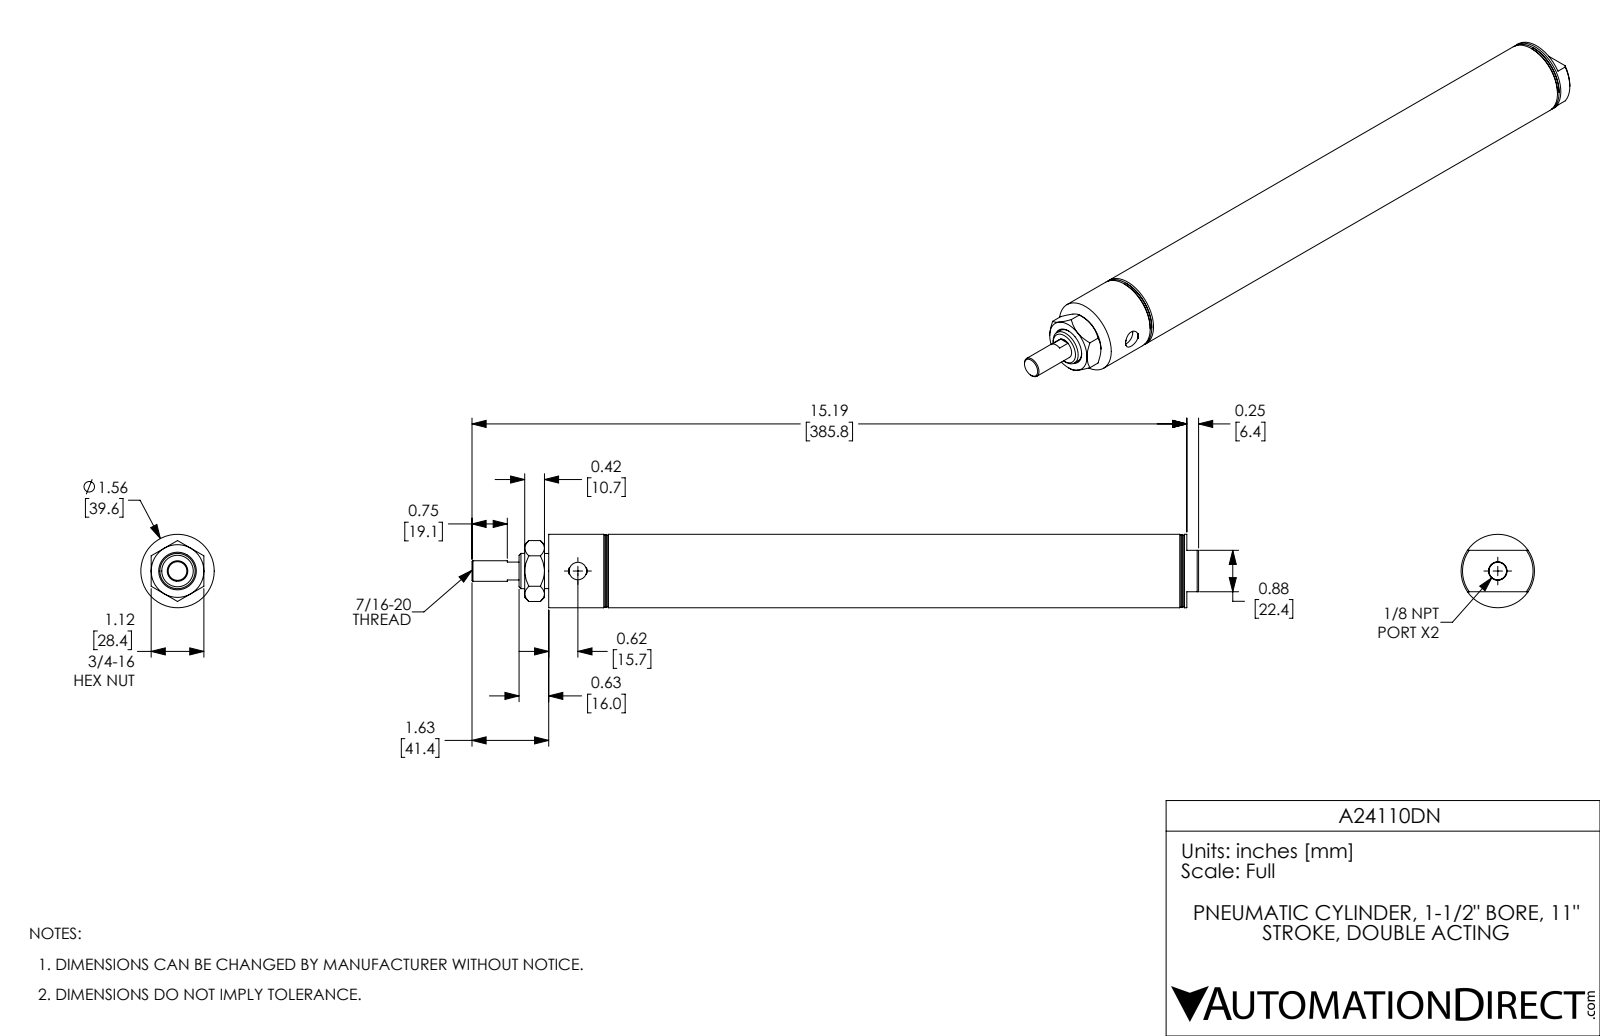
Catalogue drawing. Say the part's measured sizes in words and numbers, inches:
The part is named "A24110DN; A24110DN_Mounting Nut_D-3556; A24110DN-Rod; A24110DN-MainBody". Its 3-D file was written by "SolidWorks 2017 (AUTOMOTIVE_DESIGN)". It is 3 solids with 104 faces: 32 planar, 24 cylindrical and 48 other. Overall it measures 15.44 by 1.56 by 1.56 inches. Its volume is 9.084 cubic inches and its surface area 162.5 square inches. Round holes: 2 of diameter 0.374, 1 of diameter 0.437, 1 of diameter 0.75, 1 of diameter 1.5. Round bosses or shafts: 1 of diameter 1.56, 1 of diameter 0.746. The main face-to-face distances are 11.5, 0.5, 11, 12.84, 12.34, 1.34, 0.97, 1.47, 12.47, 13.81.
